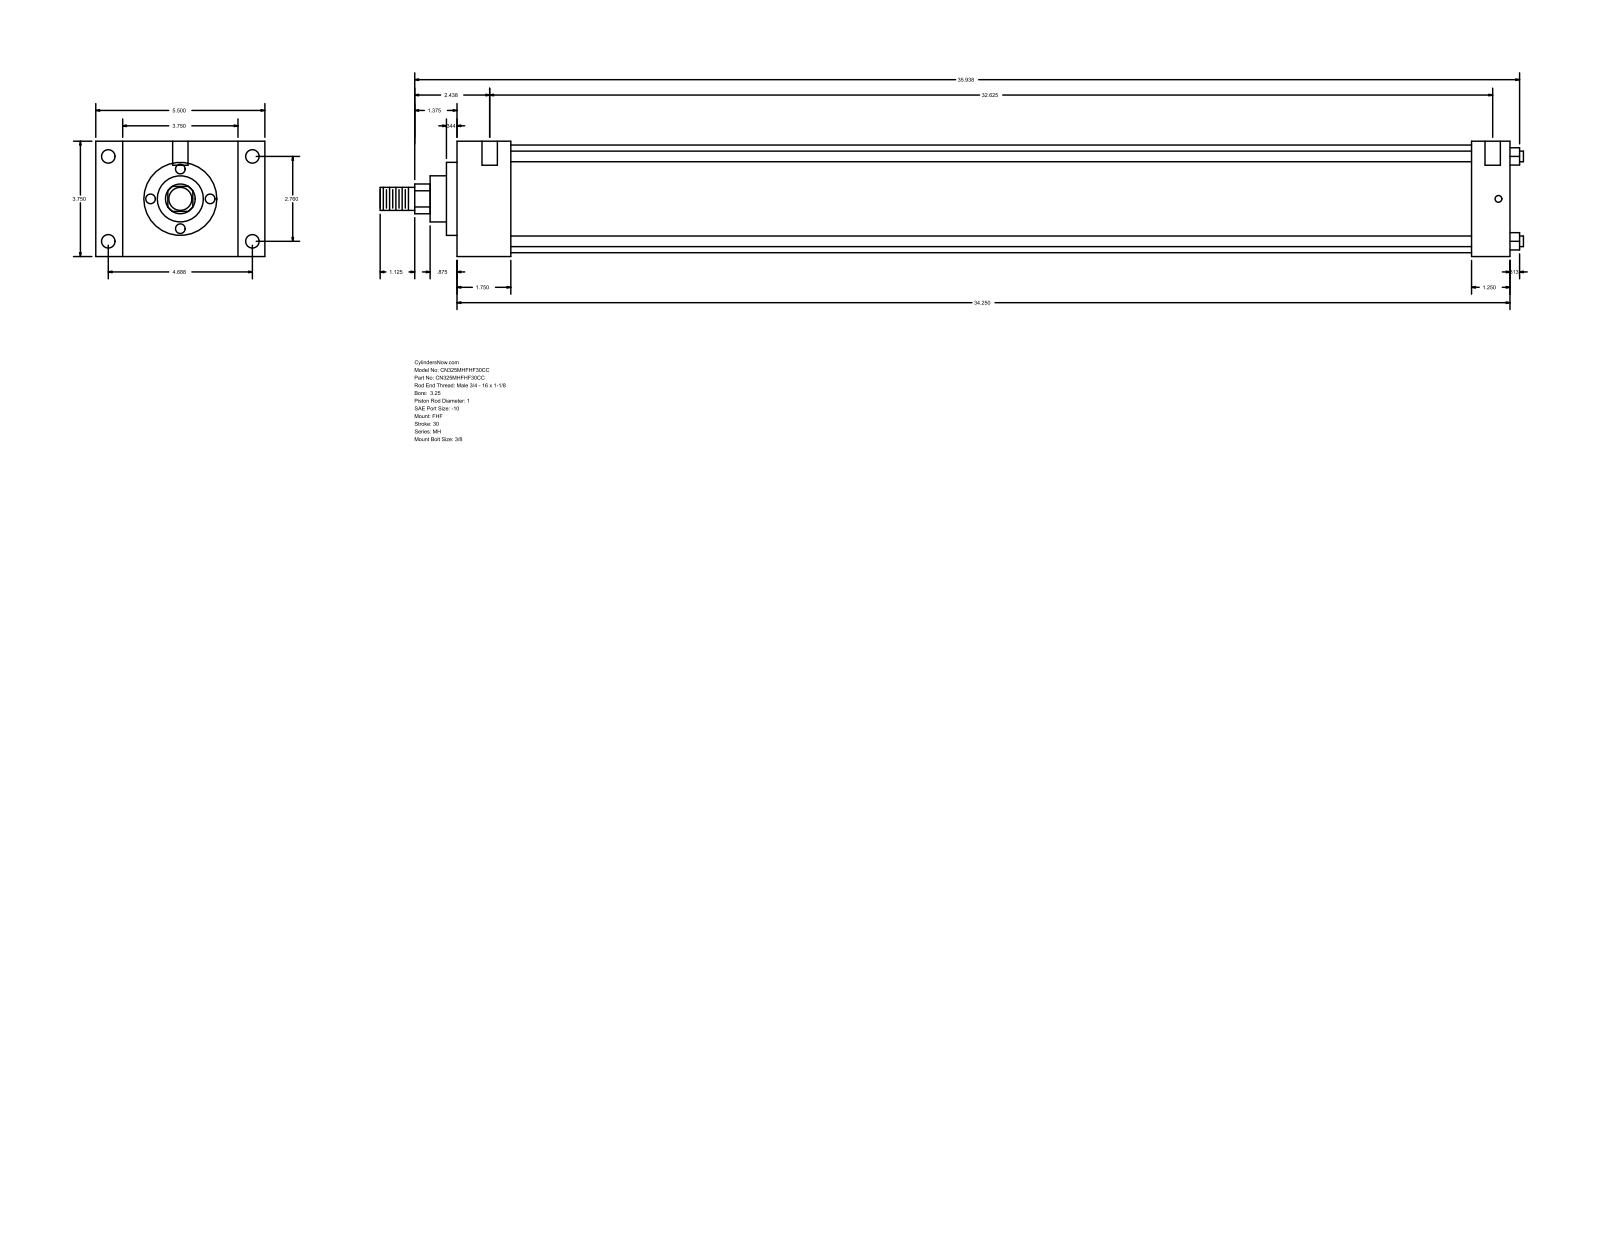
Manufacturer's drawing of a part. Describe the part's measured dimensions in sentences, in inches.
The part is named "MH_FHF__0325_1". Its 3-D file was written by "GSSL Pune (CONFIG_CONTROL_DESIGN)". It is 0 solids with 90 faces: 61 planar, 29 cylindrical and 0 other. Overall it measures 37.187 by 5.5 by 3.75 inches. Round holes: 4 of diameter 0.219, 4 of diameter 0.438, 2 of diameter 0.5. Round bosses or shafts: 4 of diameter 0.345, 1 of diameter 3.5, 1 of diameter 2.375, 1 of diameter 1.5, 1 of diameter 1, 1 of diameter 0.75. Partial cylindrical surfaces (rounded edges, fillets, slot ends): 1 of radius 0.484. The main face-to-face distances are 3.75, 34.25, 1.75, 32.5, 0.875, 4.625, 5.5, 33, 31.25, 1.25. The hole center spacings are 2.76, 4.687, 5.439, 32.875, 0.062, 0.187, 32.625, 32.687.
